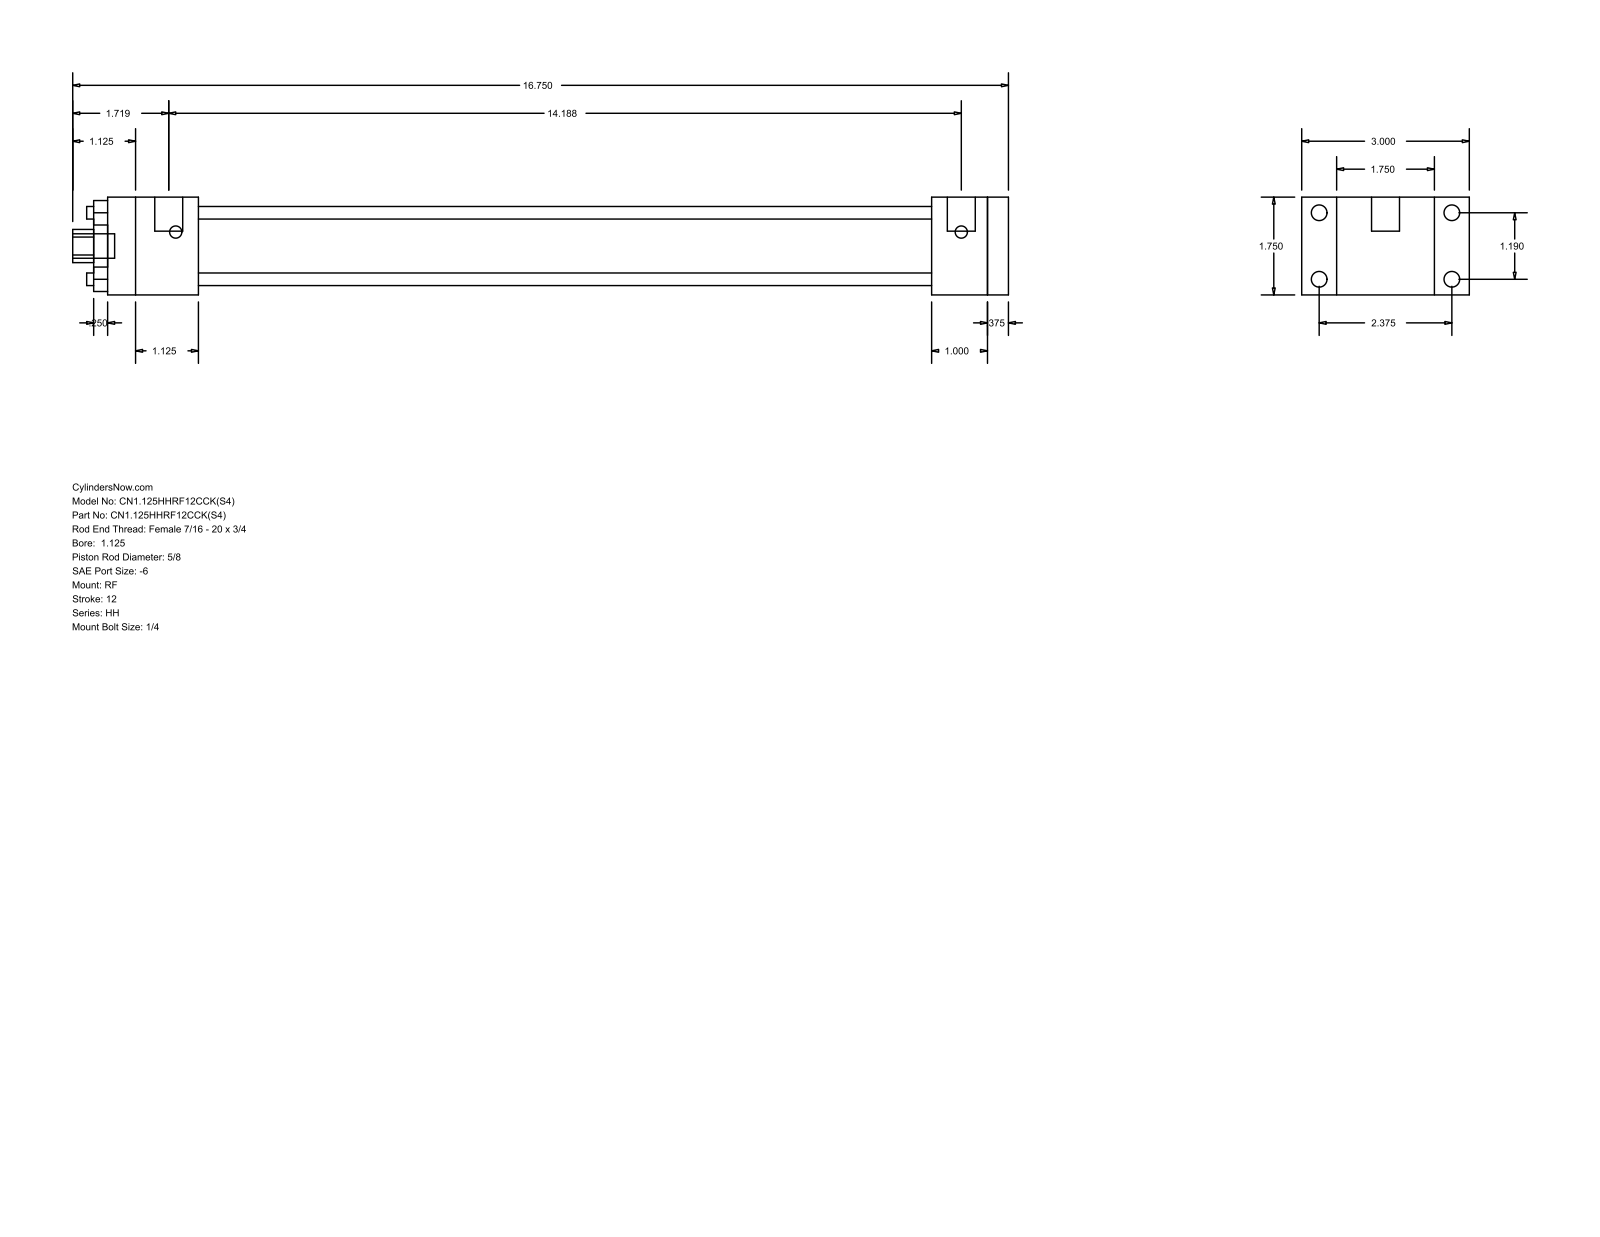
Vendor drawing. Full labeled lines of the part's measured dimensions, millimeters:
Part name (STEP PRODUCT): HH_RF__0112_0.625
STEP written by: GSSL Pune (CONFIG_CONTROL_DESIGN)
Units: millimetres
Bodies: 0 solids, 92 faces (64 planar, 28 cylindrical, 0 other)
Overall size (bounding box): 425.45 × 76.2 × 44.45
Round holes (diameter × count): ⌀5.71 ×4, ⌀15.88 ×1, ⌀28.57 ×1, ⌀34.92 ×1
Round bosses / shafts (diameter × count): ⌀7.14 ×4, ⌀5.56 ×4, ⌀12.7 ×2, ⌀11.11 ×1
Partial cylindrical surfaces — rounded edges, fillets, slot ends (radius × count): R7.54 ×1
Main face-to-face distances: 44.46, 9.52, 15.87, 358.78, 368.3, 333.37, 25.41, 34.93, 41.27, 374.64
Hole centre spacings: 21.37, 30.22, 42.74
